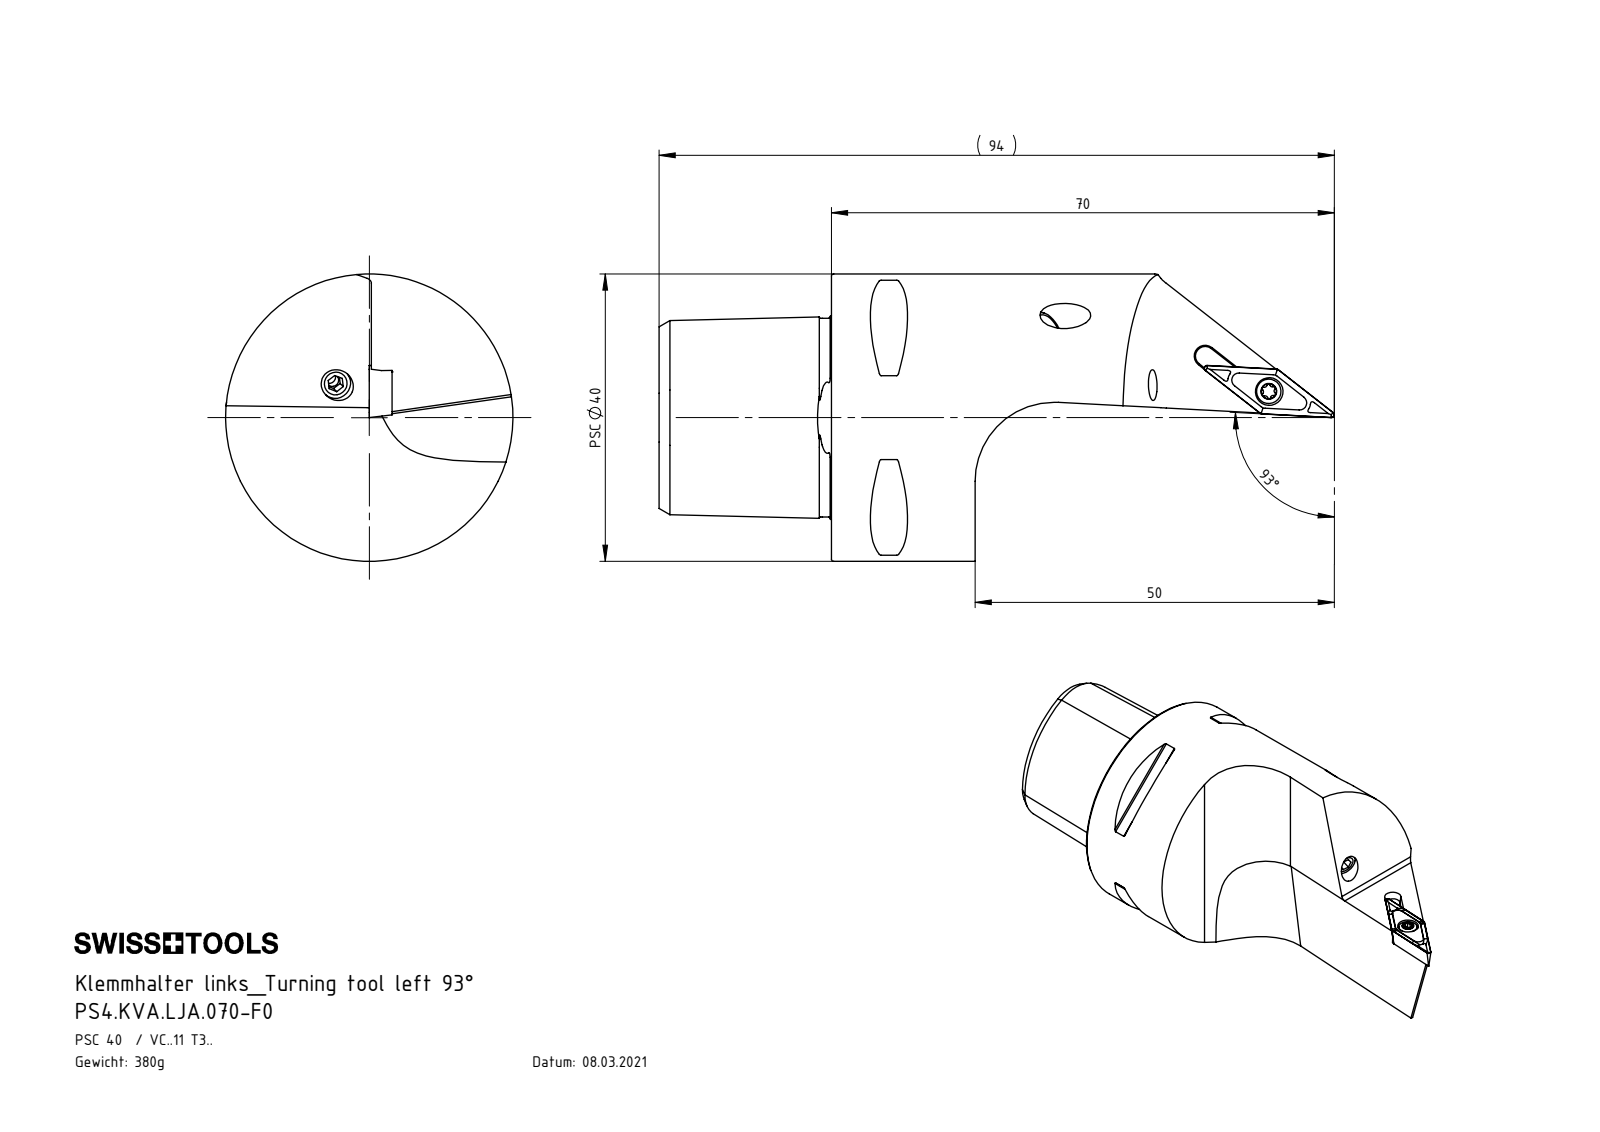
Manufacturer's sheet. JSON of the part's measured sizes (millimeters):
{"part_name": "WKX-ER1.004.005_A_PreviewCfg; KVT_MB_600_050; WCA-ER2.001.006_A; PS4-KVA.LJA.070-F0_A_Fertigbearbeitung (+2 more)", "step_written_by": "SolidWorks 2017 (AUTOMOTIVE_DESIGN)", "units": "millimeters", "bodies": {"solids": 6, "faces": 214, "planar": 63, "cylindrical": 47, "other": 104}, "overall_size": [93.98, 40, 40], "volume_mm3": 48310, "surface_area_mm2": 13275, "round_holes": [[4, 2], [4.2, 2], [1.7, 1], [2.05, 1], [2.8, 1], [3.3, 1], [3.85, 1], [4.6, 1], [5, 1], [12.5, 1], [18, 1], [20, 1]], "round_bosses_or_shafts": [[40, 1], [5, 1], [4, 1], [3.4, 1], [2.5, 1]], "partial_cylinders_radius": [[0.3, 8], [0.21, 6], [0.36, 4], [0.36, 2], [11, 2], [0.8, 1], [1.35, 1], [3, 1]], "face_to_face_distances": [20, 24, 44, 15.52, 2.88, 35.3, 15, 9, 29, 23.8], "hole_center_spacings": [23.5, 49.02, 49.08, 72.47, 72.53]}
